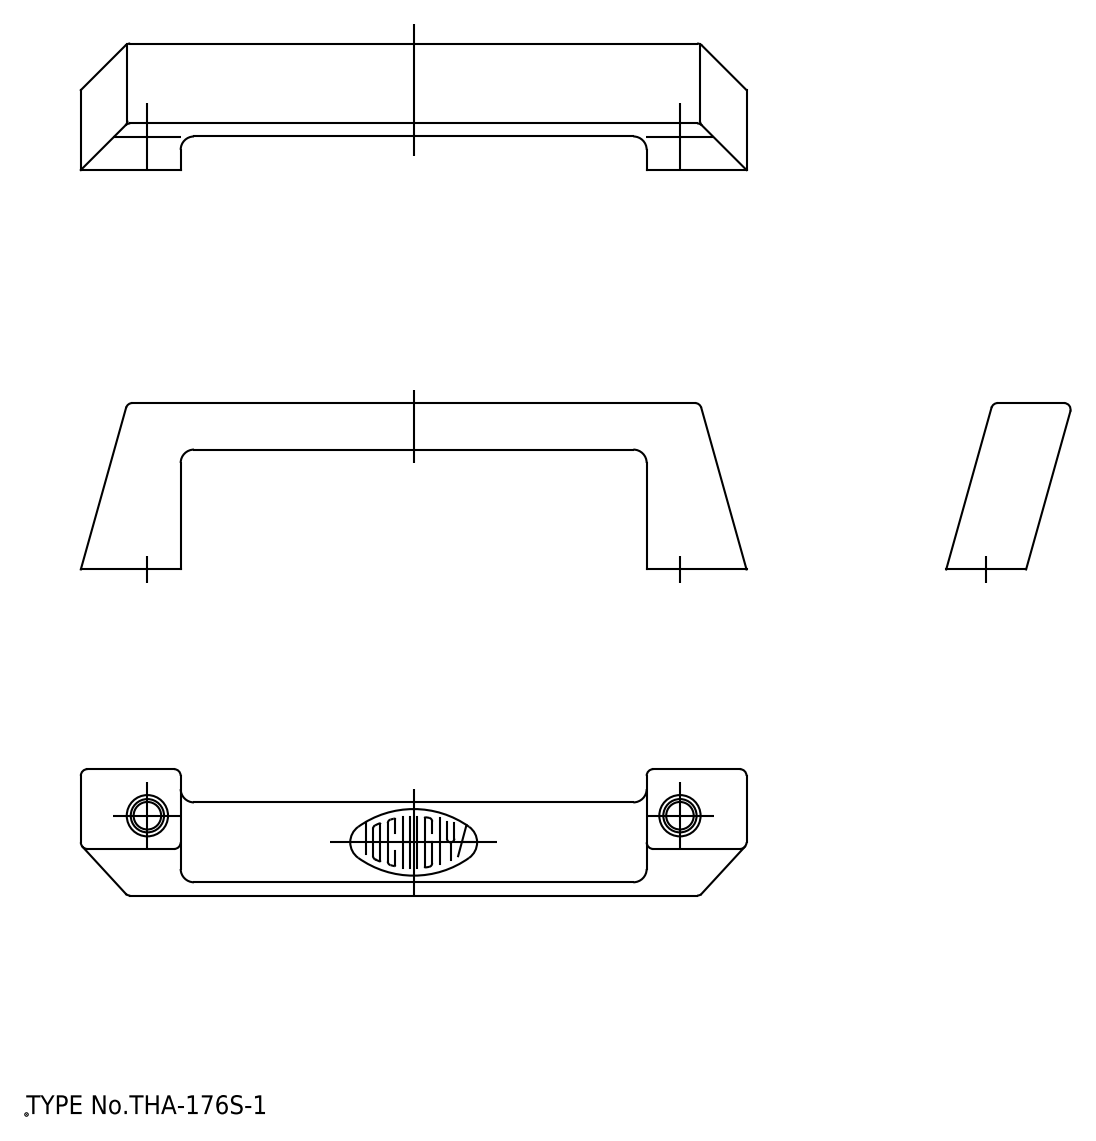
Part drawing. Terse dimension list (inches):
written by: spGate 19.8.4 (****-****-****-****) (AUTOMOTIVE_DESIGN)
unit: in
bodies: 1 solid, 40 faces (12 planar, 20 cylindrical, 8 other)
size: 3.937 × 0.984 × 0.735
volume: 0.729 in³; area: 8.438 in²
holes: 2× ⌀0.197
rounds: 14× R0.039, 2× R0.079
face distances: 0.455, 0.984, 2.756, 0.315, 0.669
hole spacings: 3.15
